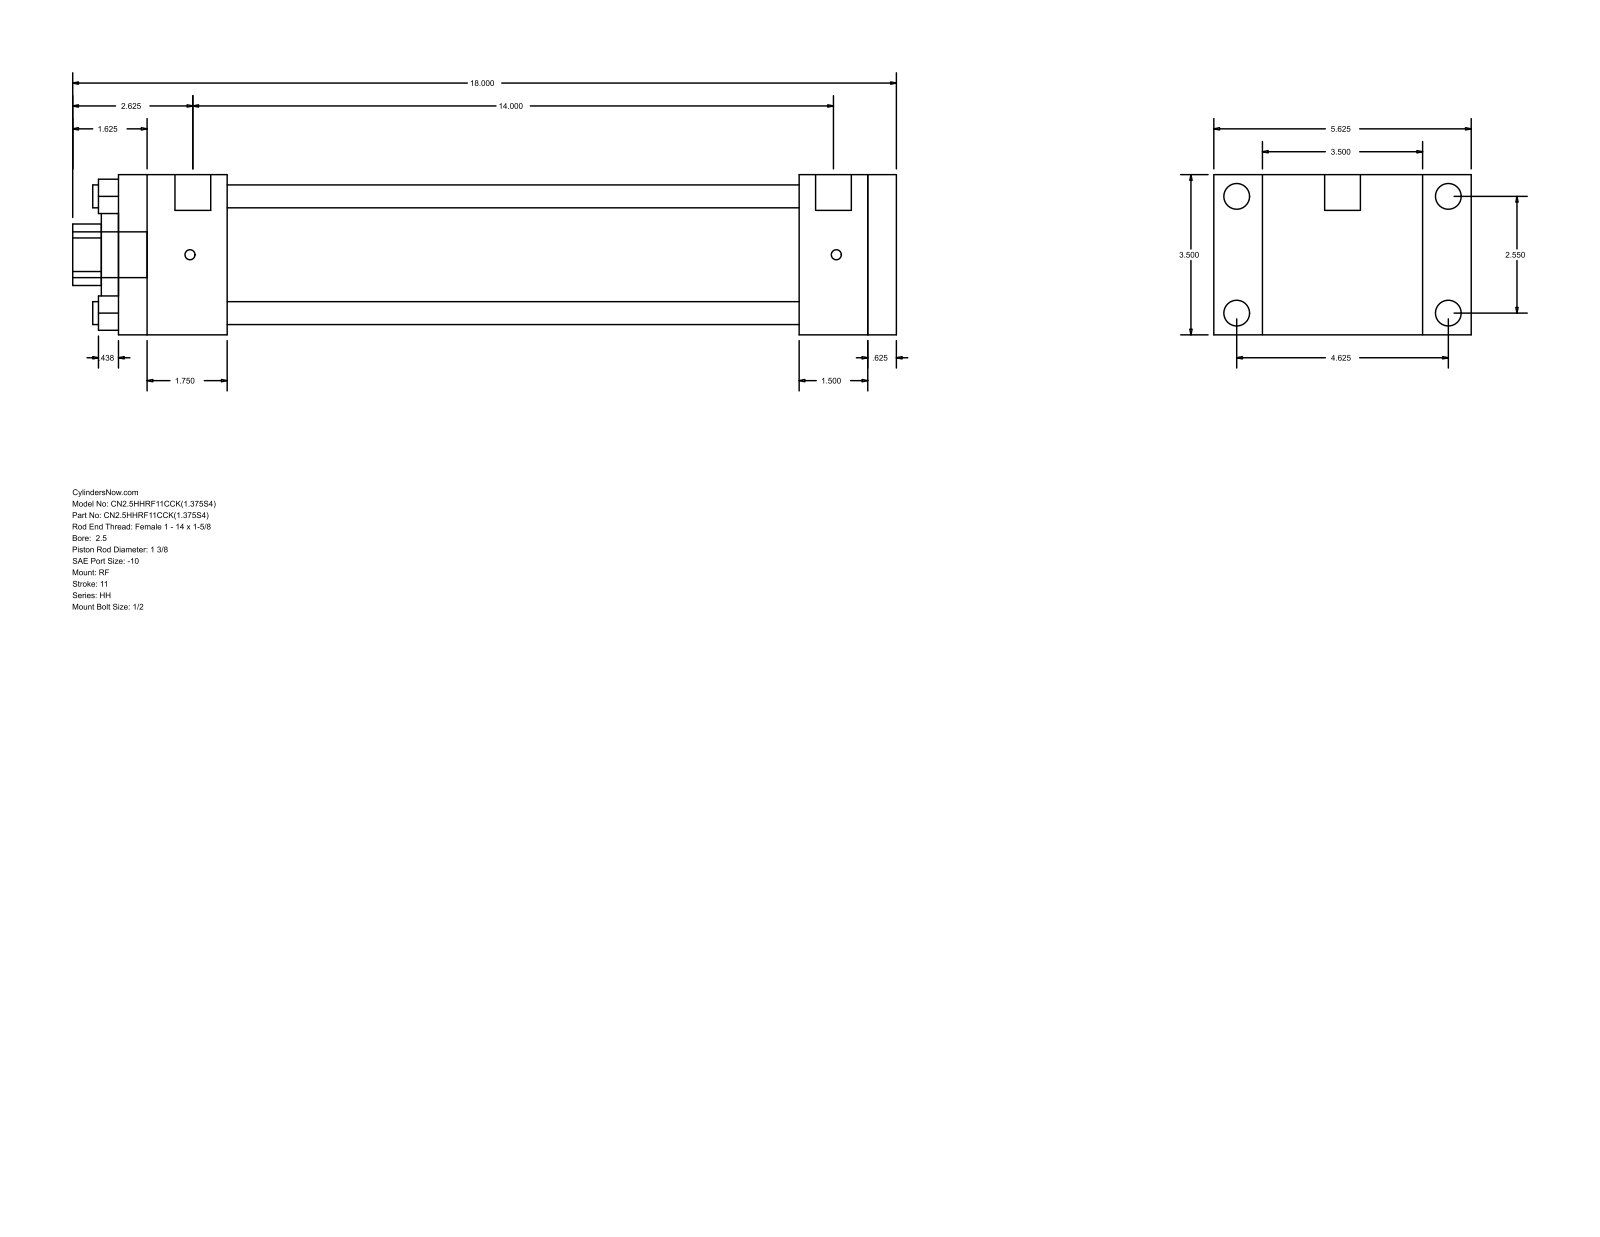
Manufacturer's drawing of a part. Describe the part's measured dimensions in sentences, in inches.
The part is named "HH_RF__0250_1.375". Its 3-D file was written by "GSSL Pune (CONFIG_CONTROL_DESIGN)". It is 0 solids with 92 faces: 64 planar, 28 cylindrical and 0 other. Overall it measures 18 by 5.625 by 3.5 inches. Round holes: 4 of diameter 0.5, 1 of diameter 1.375, 1 of diameter 2, 1 of diameter 2.875. Round bosses or shafts: 4 of diameter 0.563, 4 of diameter 0.219, 2 of diameter 0.781, 1 of diameter 1. Partial cylindrical surfaces (rounded edges, fillets, slot ends): 1 of radius 0.672. The main face-to-face distances are 3.5, 17, 0.625, 16.375, 2.375, 14, 14.625, 14.875, 12.5, 1.5. The hole center spacings are 1.803, 2.55, 3.606.
